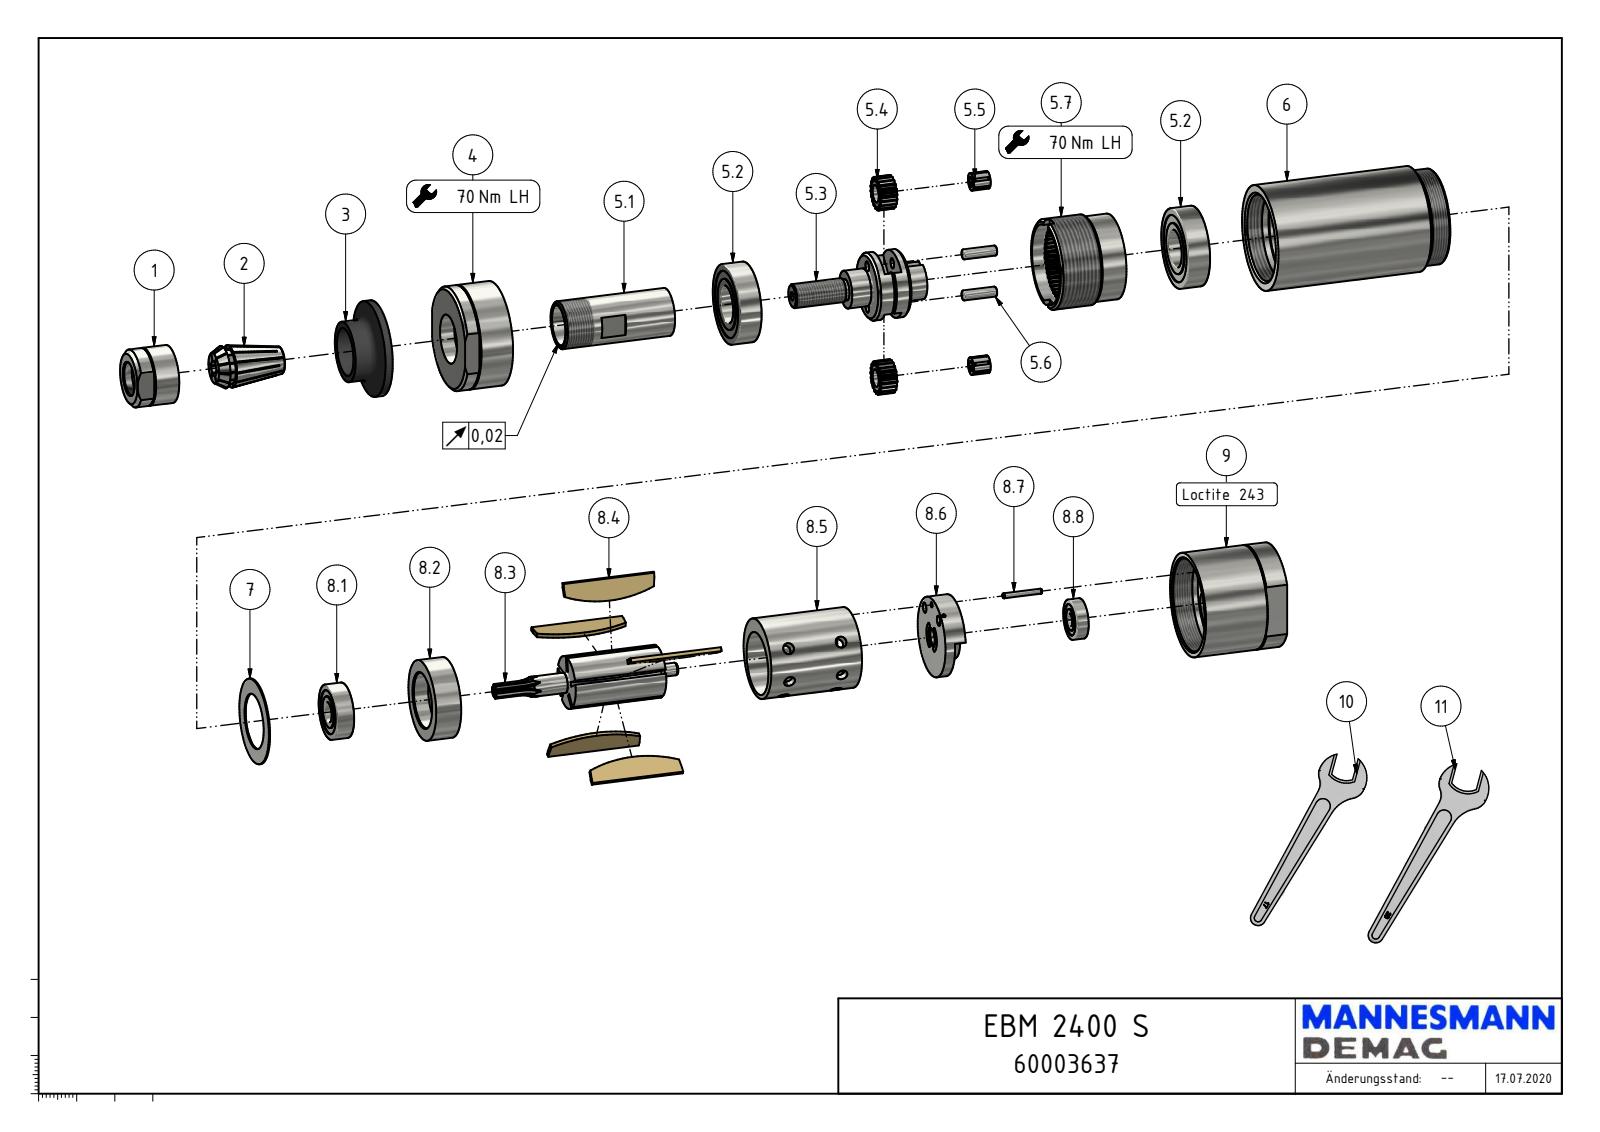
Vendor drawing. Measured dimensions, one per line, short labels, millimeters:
name: EBM 2400 S_60003637
written by: Autodesk Inventor 2024 (AUTOMOTIVE_DESIGN)
unit: mm
bodies: 1 solid, 285 faces (162 planar, 51 cylindrical, 72 other)
size: 168.42 × 42 × 42
volume: 181 113 mm³; area: 27 238 mm²
holes: 2× ⌀11.45, 1× ⌀1.6, 1× ⌀6, 1× ⌀10.5, 1× ⌀13.2, 1× ⌀17.92, 1× ⌀19.2, 1× ⌀20.3
bosses: 1× ⌀42, 1× ⌀41.5, 1× ⌀38, 1× ⌀37.99, 1× ⌀34.56, 1× ⌀24, 1× ⌀23, 1× ⌀19
rounds: 6× R18.09, 6× R33.72
face distances: 0.5, 17.75, 18.25, 120, 21.25, 98.75, 20.6, 116.88, 95.63, 3.12
hole spacings: 10.5, 11.72, 20.12
